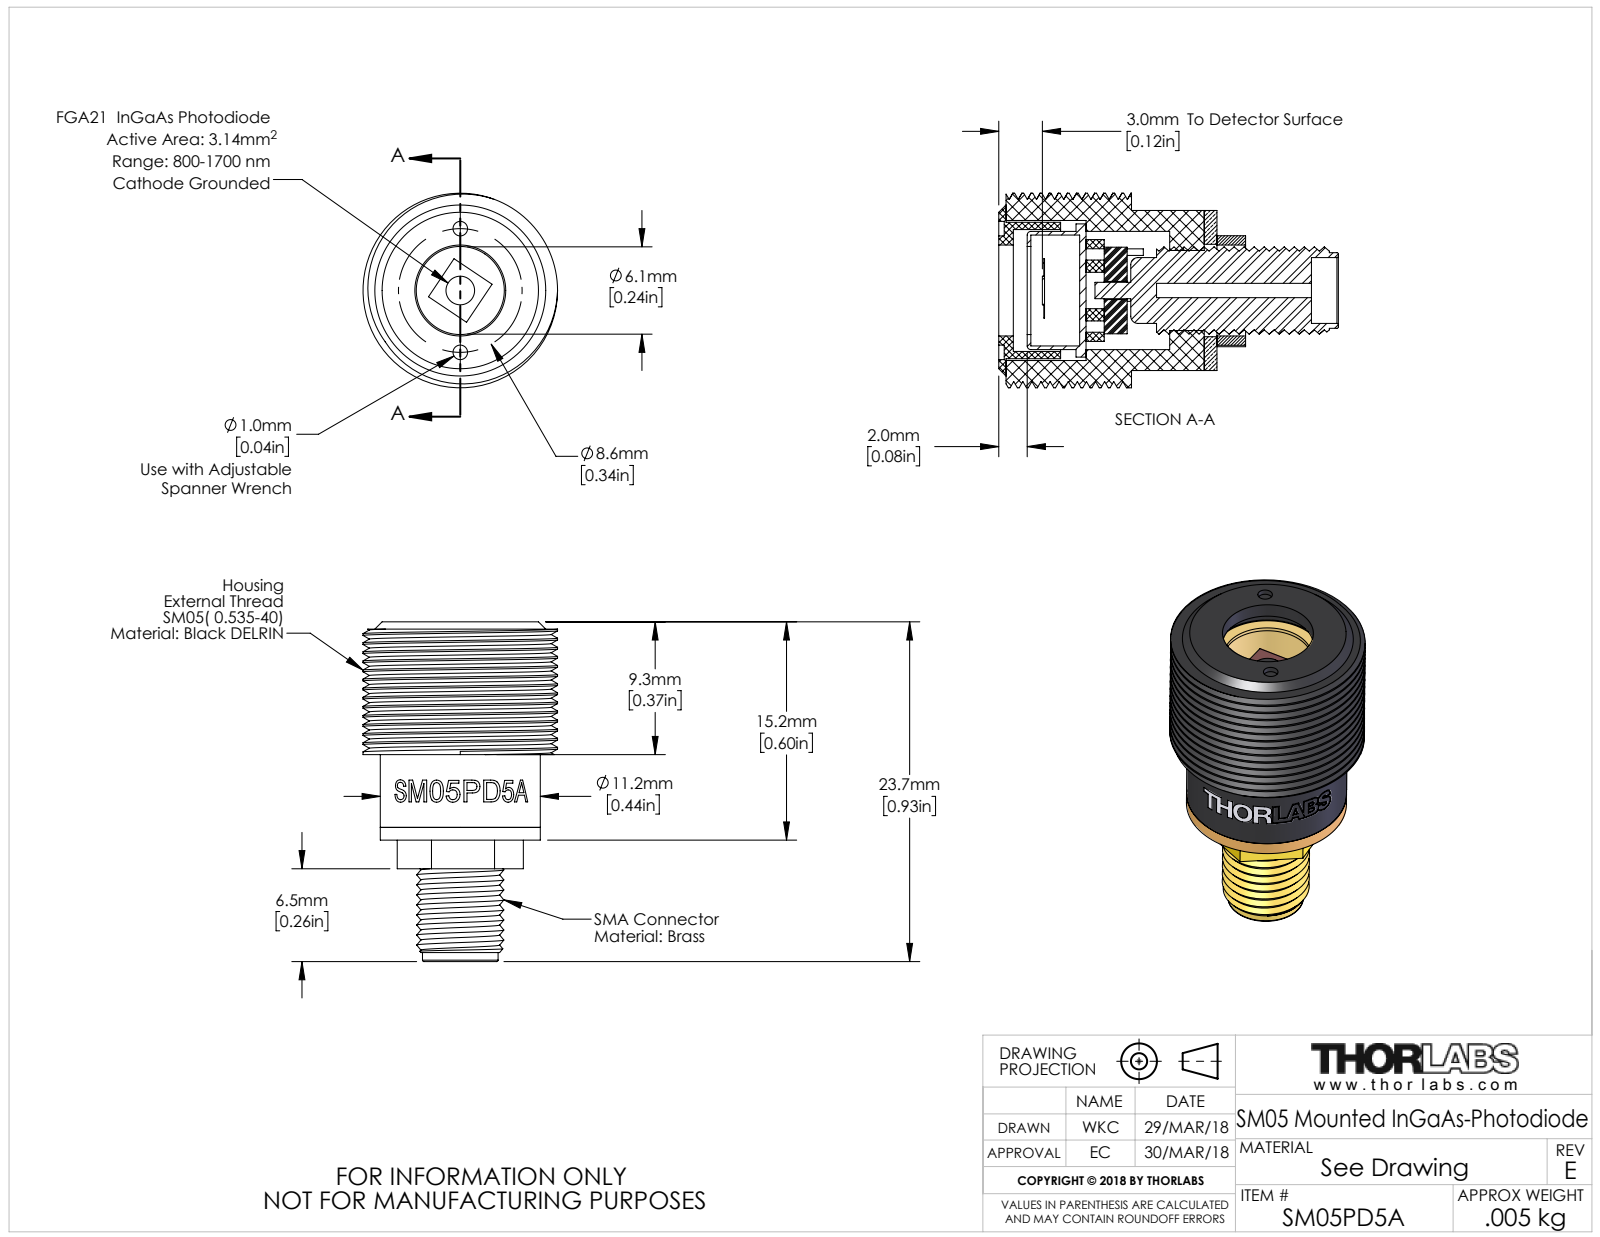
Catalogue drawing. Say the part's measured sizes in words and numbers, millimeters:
The part is named "13829-E0W". Its 3-D file was written by "SolidWorks 2016 (AUTOMOTIVE_DESIGN)". It is 7 solids with 111 faces: 46 planar, 51 cylindrical and 14 other. Overall it measures 23.5 by 13.6 by 13.6 millimeters. Its volume is 1 400 cubic millimeters and its surface area 2 889 square millimeters. Round holes: 2 of diameter 1, 1 of diameter 1, 1 of diameter 4.6, 1 of diameter 5.6, 1 of diameter 6.1, 1 of diameter 6.4, 1 of diameter 6.5, 1 of diameter 7.7, 1 of diameter 8.3, 1 of diameter 8.5, 1 of diameter 9.8. Round bosses or shafts: 3 of diameter 0.5, 1 of diameter 13.6, 1 of diameter 11.2, 1 of diameter 9.5, 1 of diameter 9.3, 1 of diameter 8.3, 1 of diameter 5.3, 1 of diameter 2. The main face-to-face distances are 8.5, 0.5, 0.9, 9.4, 14.7, 13.8, 5.3, 14.4, 15.2, 5.8. The hole center spacings are 4.3, 8.6.
